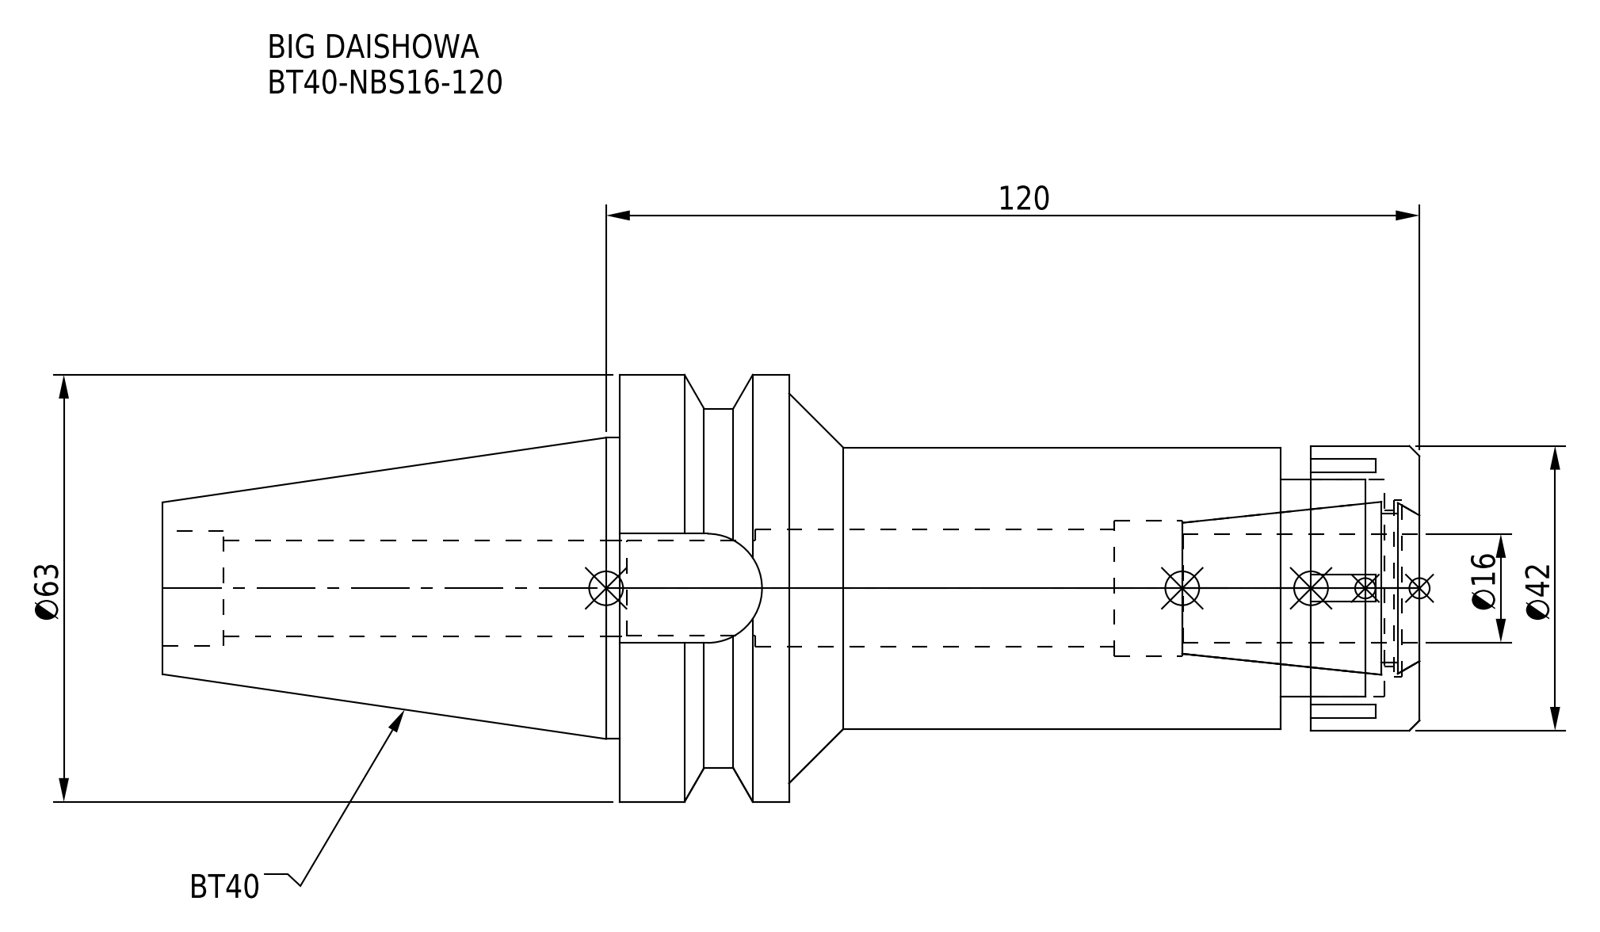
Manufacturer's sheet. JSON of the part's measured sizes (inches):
{"part_name": "BT40-NBS16-120; BT40-NBS16-120.stp; BT40-NBS16-120_1.stp; BT40-NBS16-120-FreeParts (+3 more)", "step_written_by": "SolidWorks 2019 (CONFIG_CONTROL_DESIGN)", "units": "inches", "bodies": {"solids": 2, "faces": 93, "planar": 45, "cylindrical": 34, "other": 14}, "overall_size": [7.299, 2.48, 2.48], "volume_in3": 13.25, "surface_area_in2": 67.8, "round_holes": [[0.551, 1], [0.559, 1], [0.669, 1], [0.681, 1], [0.787, 1], [0.906, 1], [1.024, 1], [1.26, 1]], "round_bosses_or_shafts": [[2.48, 1], [2.087, 1], [1.75, 1], [1.654, 1], [1.634, 1]], "partial_cylinders_radius": [[0.317, 1]], "face_to_face_distances": [4.646, 0.315, 0.807, 3.839, 0.63, 0.177, 4.016, 3.661, 3.031, 2.854]}
